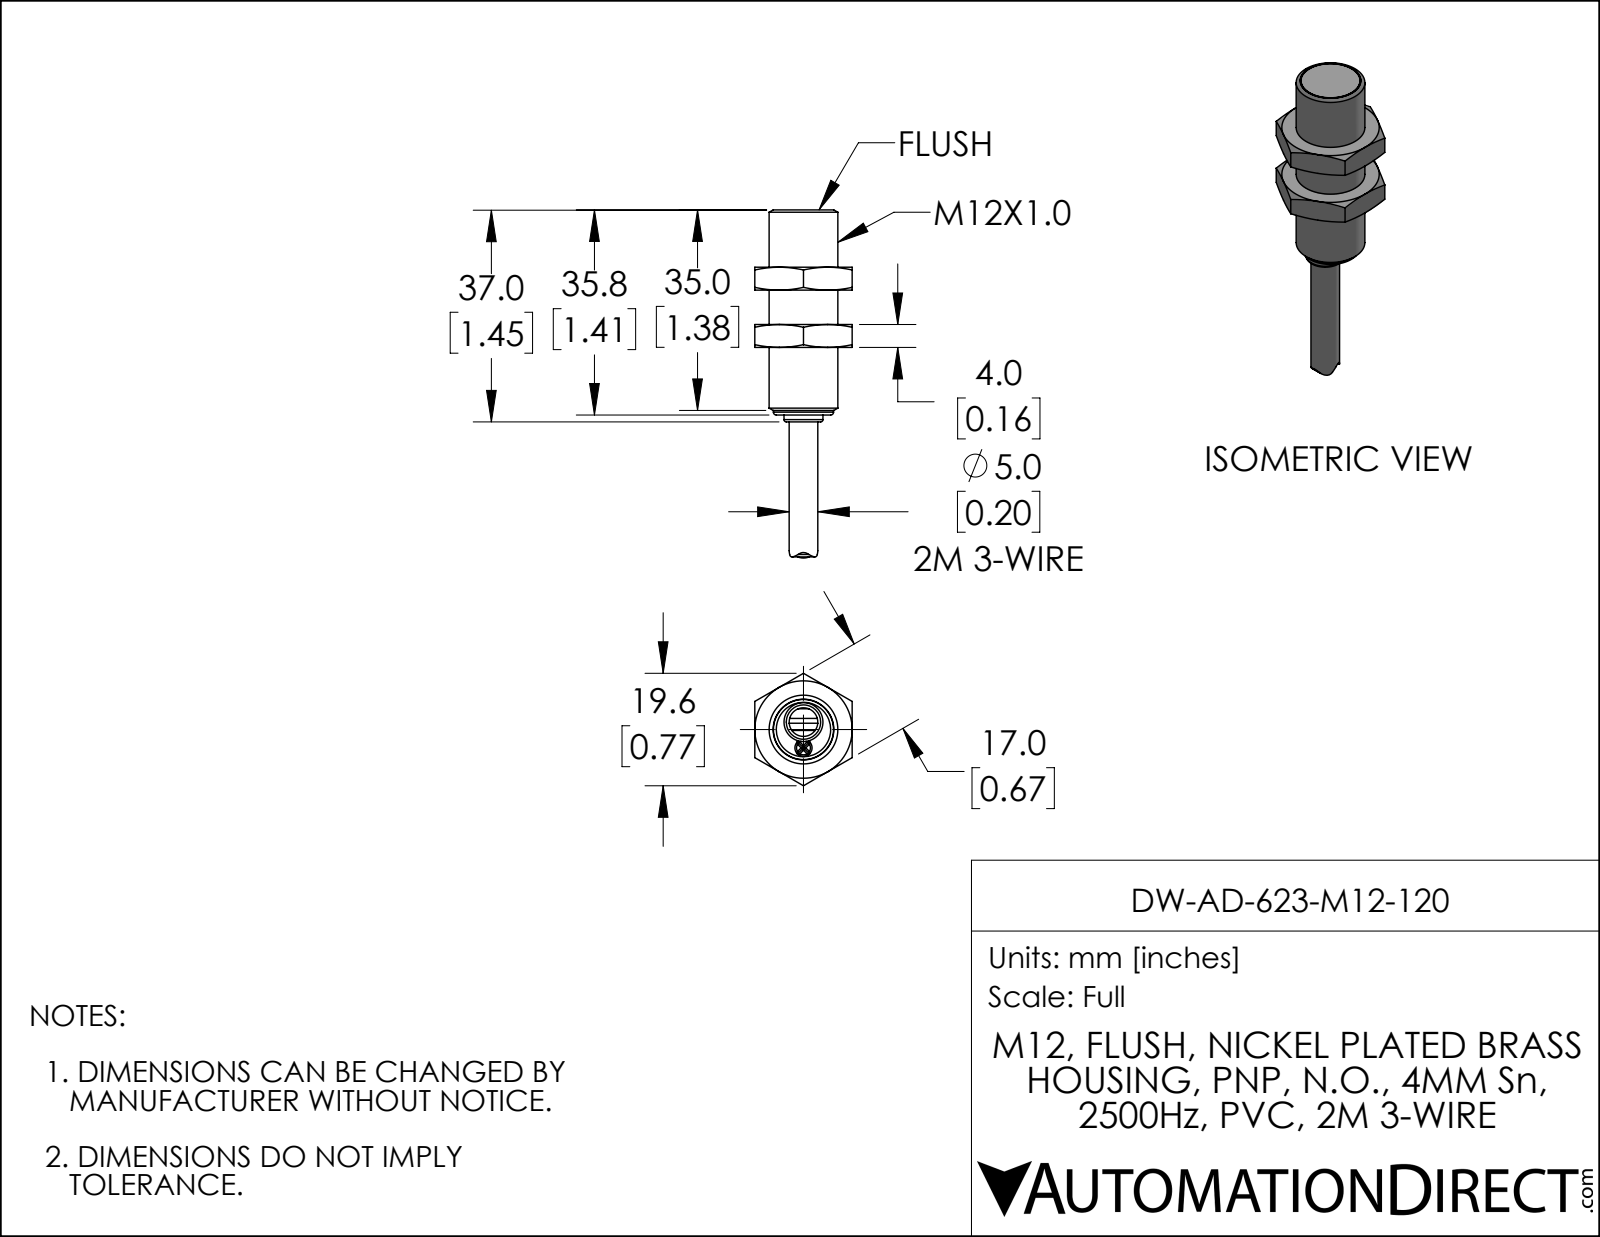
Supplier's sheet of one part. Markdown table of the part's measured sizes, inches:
| quantity | value |
| --- | --- |
| part name | DW-AD-623-M12-120 |
| STEP written by | SolidWorks 2019 (AUTOMOTIVE_DESIGN) |
| units | inches |
| bodies | 1 solid, 81 faces (34 planar, 14 cylindrical, 33 other) |
| overall size | 2.392 × 0.773 × 0.669 |
| volume | 0.342 in³ |
| surface area | 4.072 in² |
| round holes (diameter × count) | 0.415 × 1 |
| round bosses / shafts (diameter × count) | 0.472 × 1, 0.413 × 1, 0.406 × 1, 0.268 × 1, 0.197 × 1, 0.118 × 1 |
| partial cylindrical surfaces (radius × count) | 0.031 × 1, 0.041 × 1, 0.165 × 1, 0.248 × 1, 0.331 × 1 |
| main face-to-face distances | 0.394, 0.157, 0.669, 0.551, 0.236, 0.787, 0.945, 1.409, 1.016, 0.858 |
